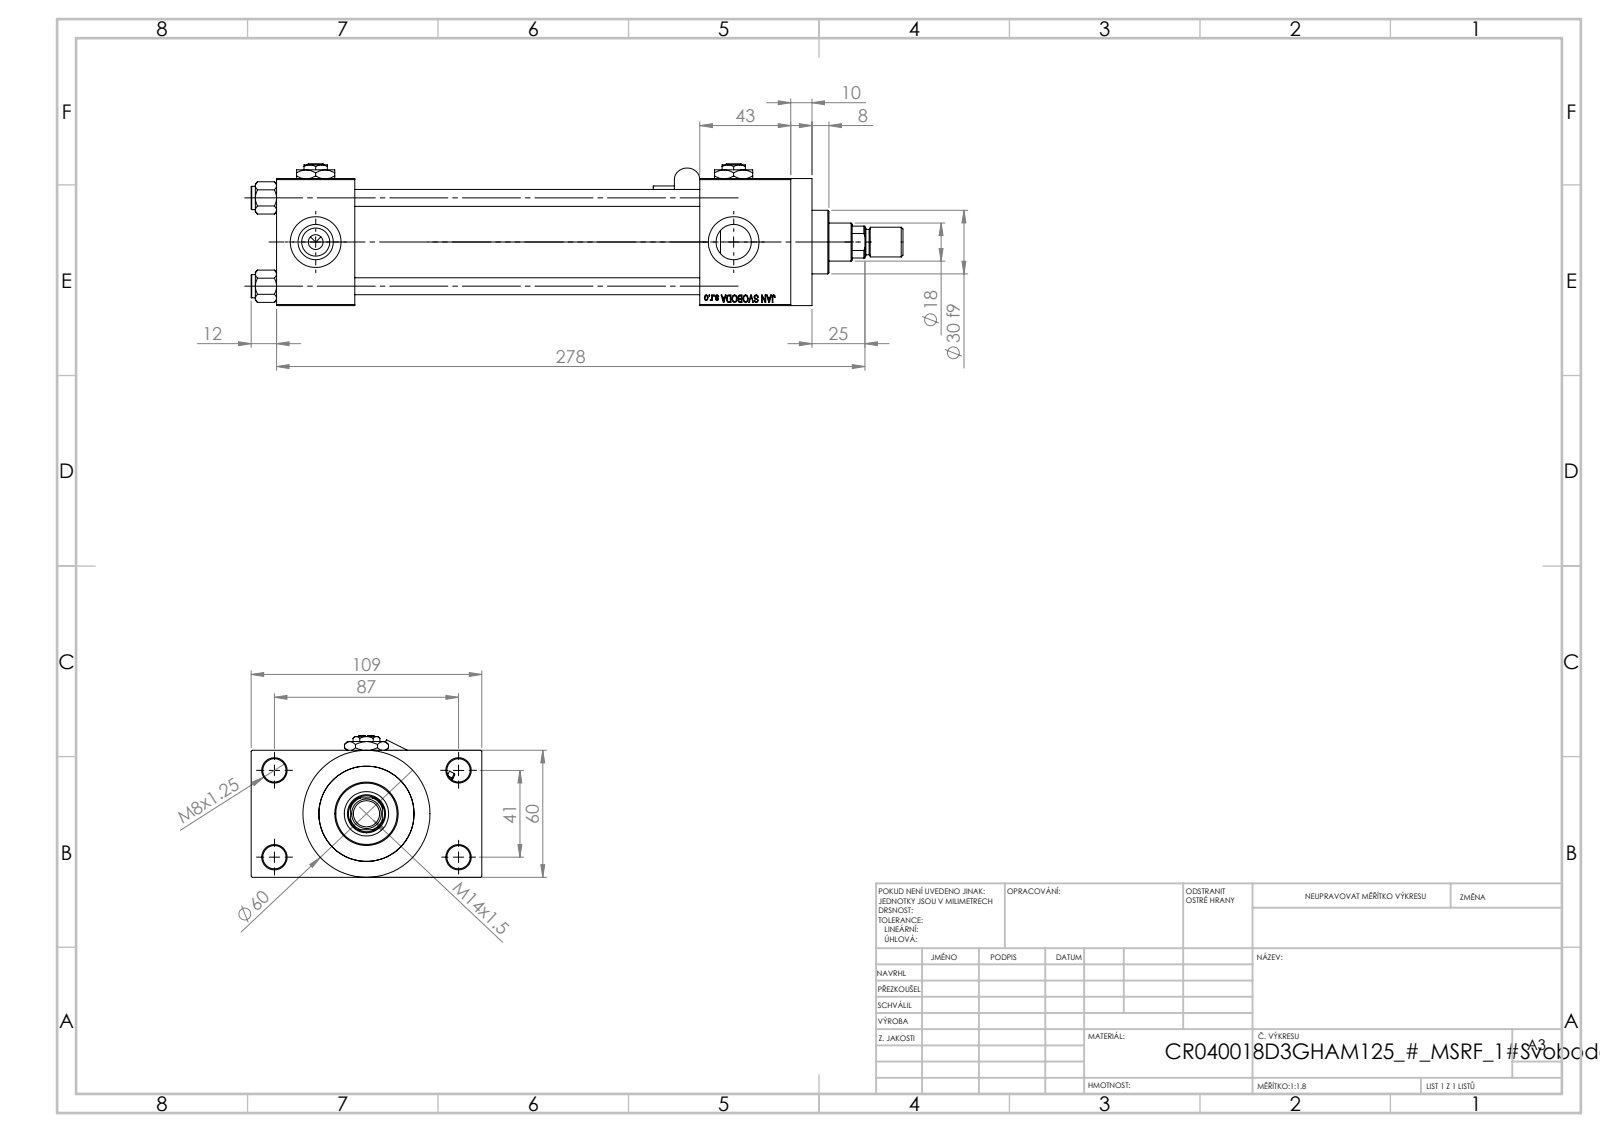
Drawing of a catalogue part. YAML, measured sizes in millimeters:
part_name: "V215CR_D_Body; NUT_M5_D; MSRF_MSRG1; Zatka_pro_OIL_PORT (+4 more)"
step_written_by: "SolidWorks 2019 (CONFIG_CONTROL_DESIGN)"
units: millimeters
bodies: {solids: 15, faces: 1251, planar: 568, cylindrical: 117, other: 566}
overall_size: [308, 109, 67]
volume: 606930
surface_area: 173326
round_holes:
  - {diameter: 8, count: 4}
  - {diameter: 11, count: 4}
  - {diameter: 16.66, count: 4}
  - {diameter: 24, count: 4}
  - {diameter: 7, count: 3}
  - {diameter: 8.5, count: 1}
  - {diameter: 18, count: 1}
  - {diameter: 21, count: 1}
  - {diameter: 31, count: 1}
  - {diameter: 40, count: 1}
  - {diameter: 45, count: 1}
round_bosses_or_shafts:
  - {diameter: 11, count: 4}
  - {diameter: 60, count: 1}
  - {diameter: 46, count: 1}
  - {diameter: 30, count: 1}
  - {diameter: 14, count: 1}
  - {diameter: 12, count: 1}
  - {diameter: 5, count: 1}
  - {diameter: 2.5, count: 1}
partial_cylinders:
  - {radius: 0.5, count: 6}
  - {radius: 6, count: 2}
  - {radius: 8.5, count: 1}
face_to_face_distances: [60, 163, 24.5, 200, 84.5, 37, 43, 243, 206, 53]
hole_center_spacings: [22.65, 29.49, 41.7, 47.15, 48.09, 64.35, 76.49, 41]
